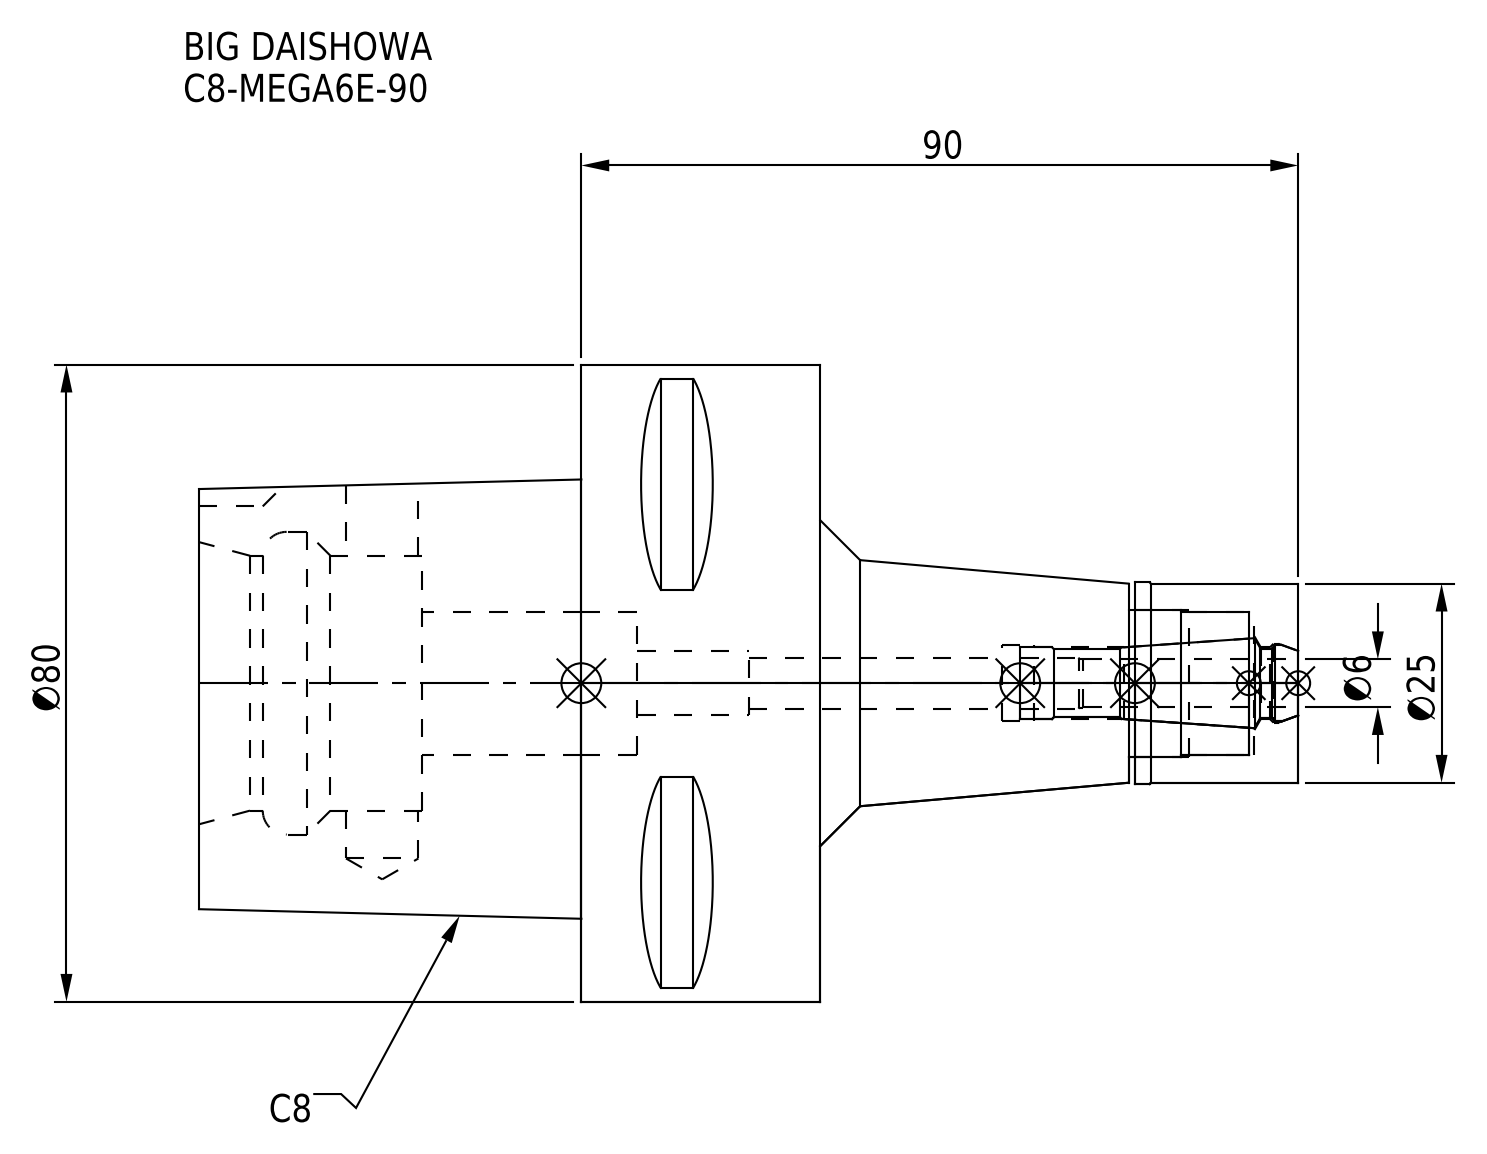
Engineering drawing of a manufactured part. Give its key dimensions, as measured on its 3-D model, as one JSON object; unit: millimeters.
{"part_name": "C8-MEGA6E-90-060-FreeParts; DXF_TEMP_ASSY_ASM_4_ASM.stp; C8-MEGA6E-90-060_ASM.stp; C8-MEGA6E-90 (+3 more)", "step_written_by": "SolidWorks 2019 (CONFIG_CONTROL_DESIGN)", "units": "millimeters", "bodies": {"solids": 2, "faces": 100, "planar": 37, "cylindrical": 39, "other": 24}, "overall_size": [138, 80, 80], "volume_mm3": 254741, "surface_area_mm2": 40197, "round_holes": [[6.4, 1], [8, 1], [9, 1], [9.1, 1], [9.6, 1], [9.9, 1], [18, 1], [18.5, 1], [32, 1], [38, 1]], "round_bosses_or_shafts": [[80, 1], [25.3, 1], [25, 1]], "partial_cylinders_radius": [[6, 1]], "face_to_face_distances": [30, 78, 48, 20, 50, 28, 60, 90, 110, 138]}
